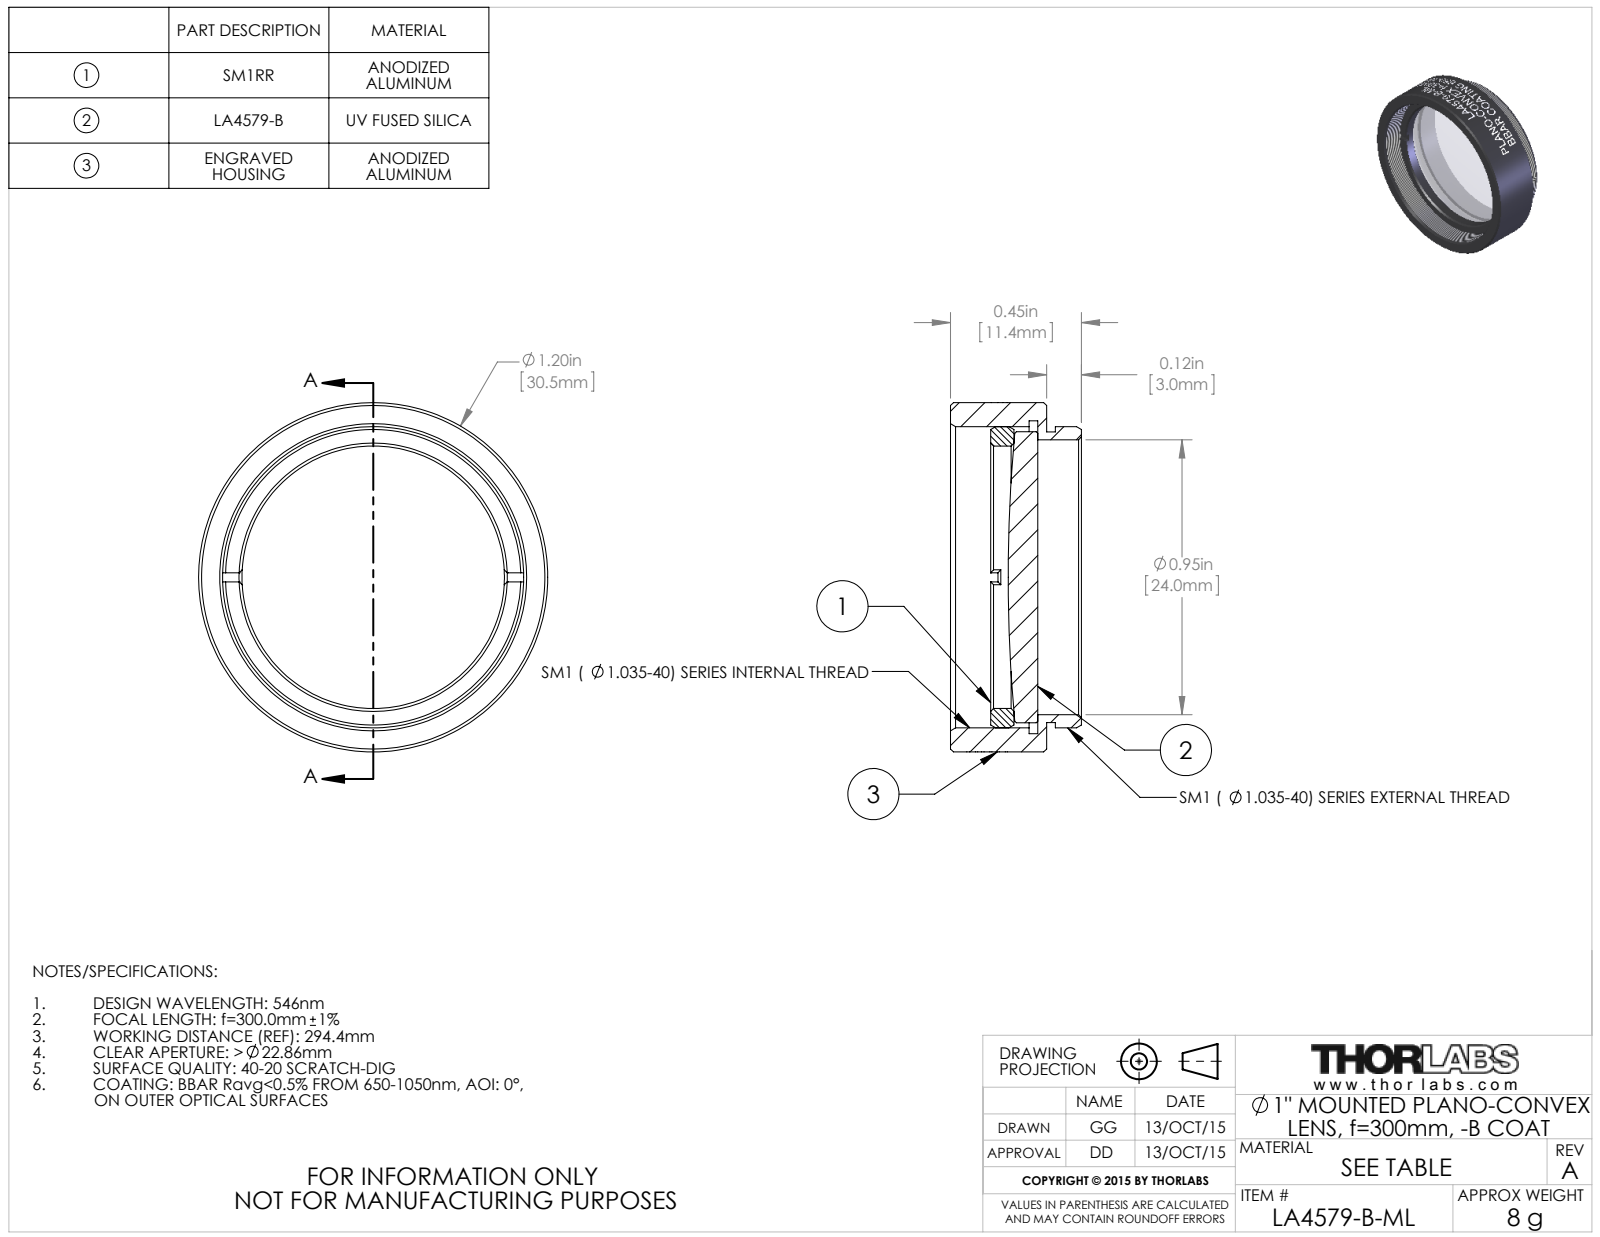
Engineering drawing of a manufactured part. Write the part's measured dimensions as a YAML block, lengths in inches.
part_name: "TTN039315-E0W"
step_written_by: "SolidWorks 2014 (CONFIG_CONTROL_DESIGN)"
units: inches
bodies: {solids: 3, faces: 164, planar: 20, cylindrical: 116, other: 28}
overall_size: [1.2, 1.2, 0.45]
volume: 0.198
surface_area: 6.667
round_holes:
  - {diameter: 0.902, count: 1}
  - {diameter: 0.945, count: 1}
  - {diameter: 1.075, count: 1}
round_bosses_or_shafts:
  - {diameter: 1.2, count: 1}
  - {diameter: 1.035, count: 1}
  - {diameter: 1, count: 1}
  - {diameter: 0.999, count: 1}
face_to_face_distances: [0.03, 0.33, 0.3, 0.137, 0.163, 0.112, 0.082, 0.218, 0.193, 0.08]
